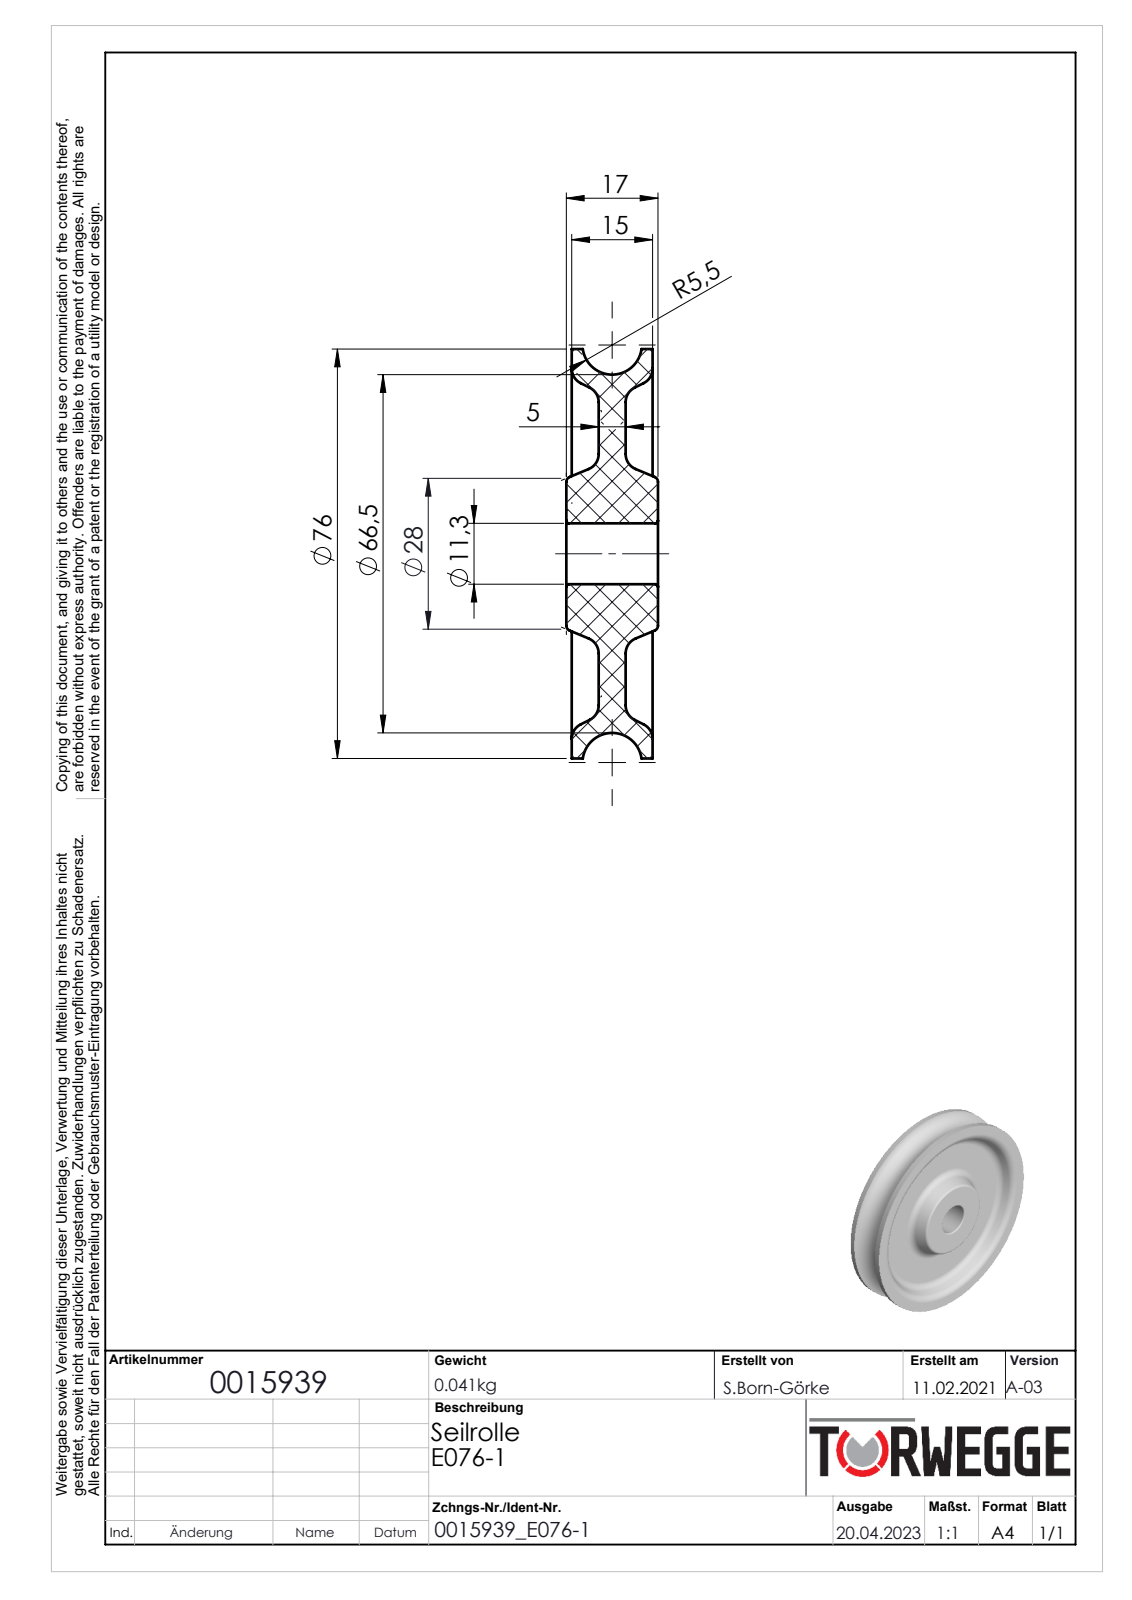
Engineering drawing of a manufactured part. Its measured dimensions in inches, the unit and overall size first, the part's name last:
Units: inches
Overall size (bounding box): 2.992 × 2.992 × 0.669
Round holes (diameter × count): ⌀0.445 ×1
Round bosses / shafts (diameter × count): ⌀2.992 ×1
Main face-to-face distances: 0.197, 0.394, 0.039, 0.236, 0.433, 0.63, 0.591, 0.669
Volume: 2.176 in³ · Surface area: 23.96 in²
Bodies: 1 solid, 44 faces (6 planar, 6 cylindrical, 32 other)
Part name (STEP PRODUCT): 0015939
STEP written by: SolidWorks 2020 (AUTOMOTIVE_DESIGN)
